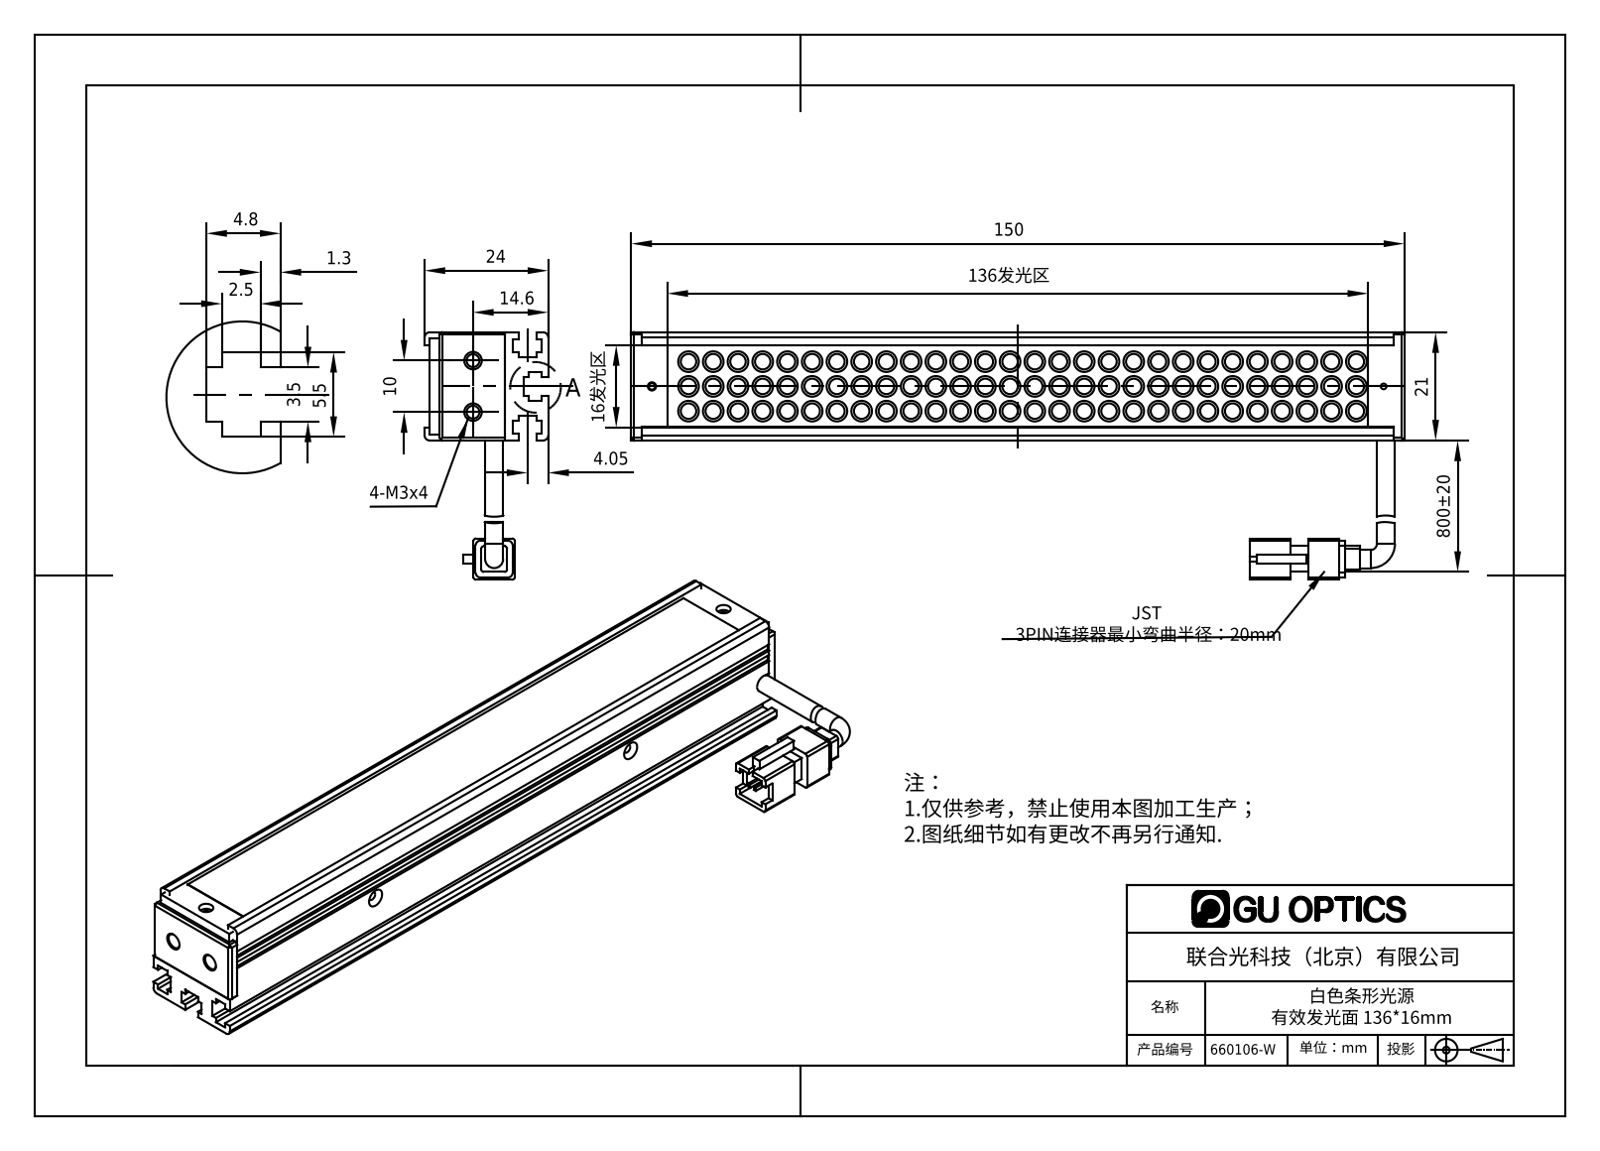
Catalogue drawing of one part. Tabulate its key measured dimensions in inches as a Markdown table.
| quantity | value |
| --- | --- |
| part name | 660106-W |
| STEP written by | SolidWorks 2016 (AUTOMOTIVE_DESIGN) |
| units | inches |
| bodies | 8 solids, 941 faces (335 planar, 419 cylindrical, 187 other) |
| overall size | 5.906 × 1.89 × 0.945 |
| volume | 2.664 in³ |
| surface area | 75.43 in² |
| round holes (diameter × count) | 0.063 × 5, 0.059 × 2, 0.067 × 2, 0.098 × 2, 0.11 × 2, 0.118 × 2, 0.043 × 1, 0.049 × 1, 0.079 × 1 |
| round bosses / shafts (diameter × count) | 0.157 × 84, 0.118 × 84, 0.138 × 2 |
| partial cylindrical surfaces (radius × count) | 0.039 × 12, 0.02 × 8, 0.065 × 1 |
| main face-to-face distances | 0.039, 0.098, 0.079, 0.579, 0.728, 0.157, 0.083, 0.575, 0.051, 0.138 |
| hole center spacings | 5.591, 0.276, 1.419, 1.433, 4.174, 4.179, 5.597, 0.394 |
